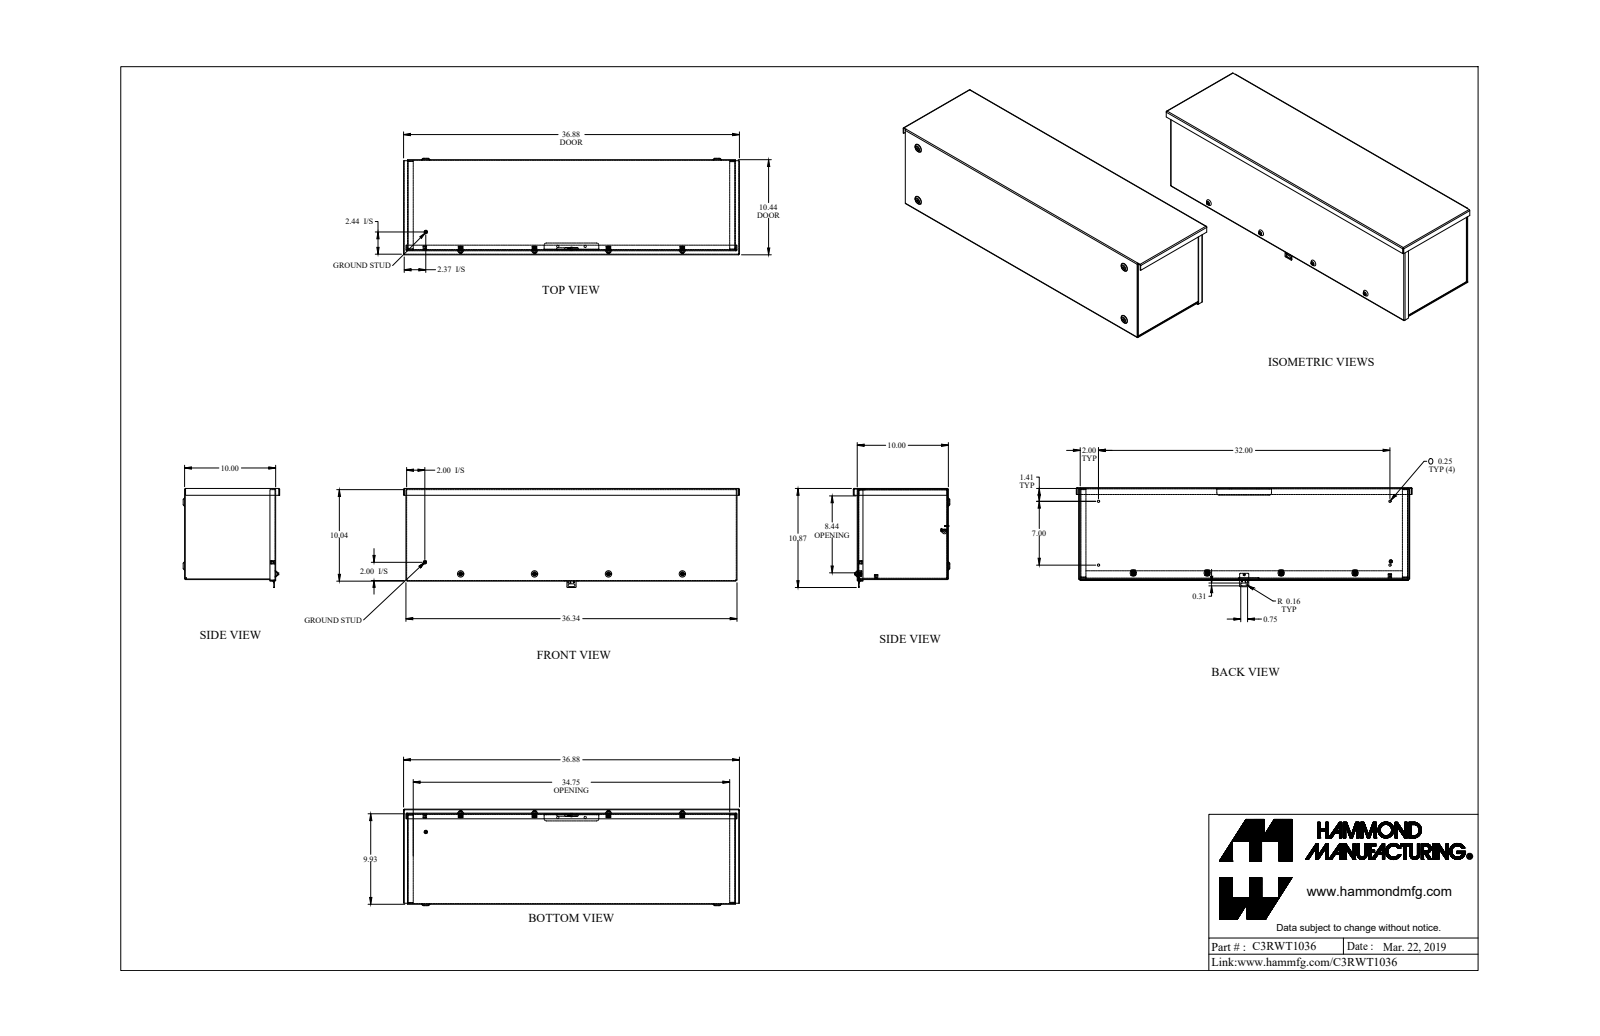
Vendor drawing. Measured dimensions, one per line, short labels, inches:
name: C3RWT1036_Default
written by: SolidWorks 2019 (CONFIG_CONTROL_DESIGN)
unit: in
bodies: 25 solids, 885 faces (486 planar, 275 cylindrical, 124 other)
size: 36.875 × 10.871 × 10.594
volume: 129.8 in³; area: 3 639 in²
holes: 6× ⌀0.156, 6× ⌀0.25, 4× ⌀0.214, 4× ⌀0.23, 2× ⌀0.203, 1× ⌀0.125, 1× ⌀0.137, 1× ⌀0.2, 1× ⌀0.215
bosses: 5× ⌀0.19, 4× ⌀0.148, 2× ⌀0.375, 1× ⌀0.5, 1× ⌀0.367, 1× ⌀0.21, 1× ⌀0.152, 1× ⌀0.125
rounds: 18× R0.036, 18× R0.108, 16× R0.08, 16× R0.108, 12× R0.125, 8× R0.022, 6× R0.25, 4× R0.016
face distances: 0.072, 9.928, 9.856, 10, 35.928, 36, 35.856, 0.172, 0.144, 9.784
hole spacings: 10.095, 22.801, 3.927, 4.061, 5.026, 7, 7.139, 7.96
